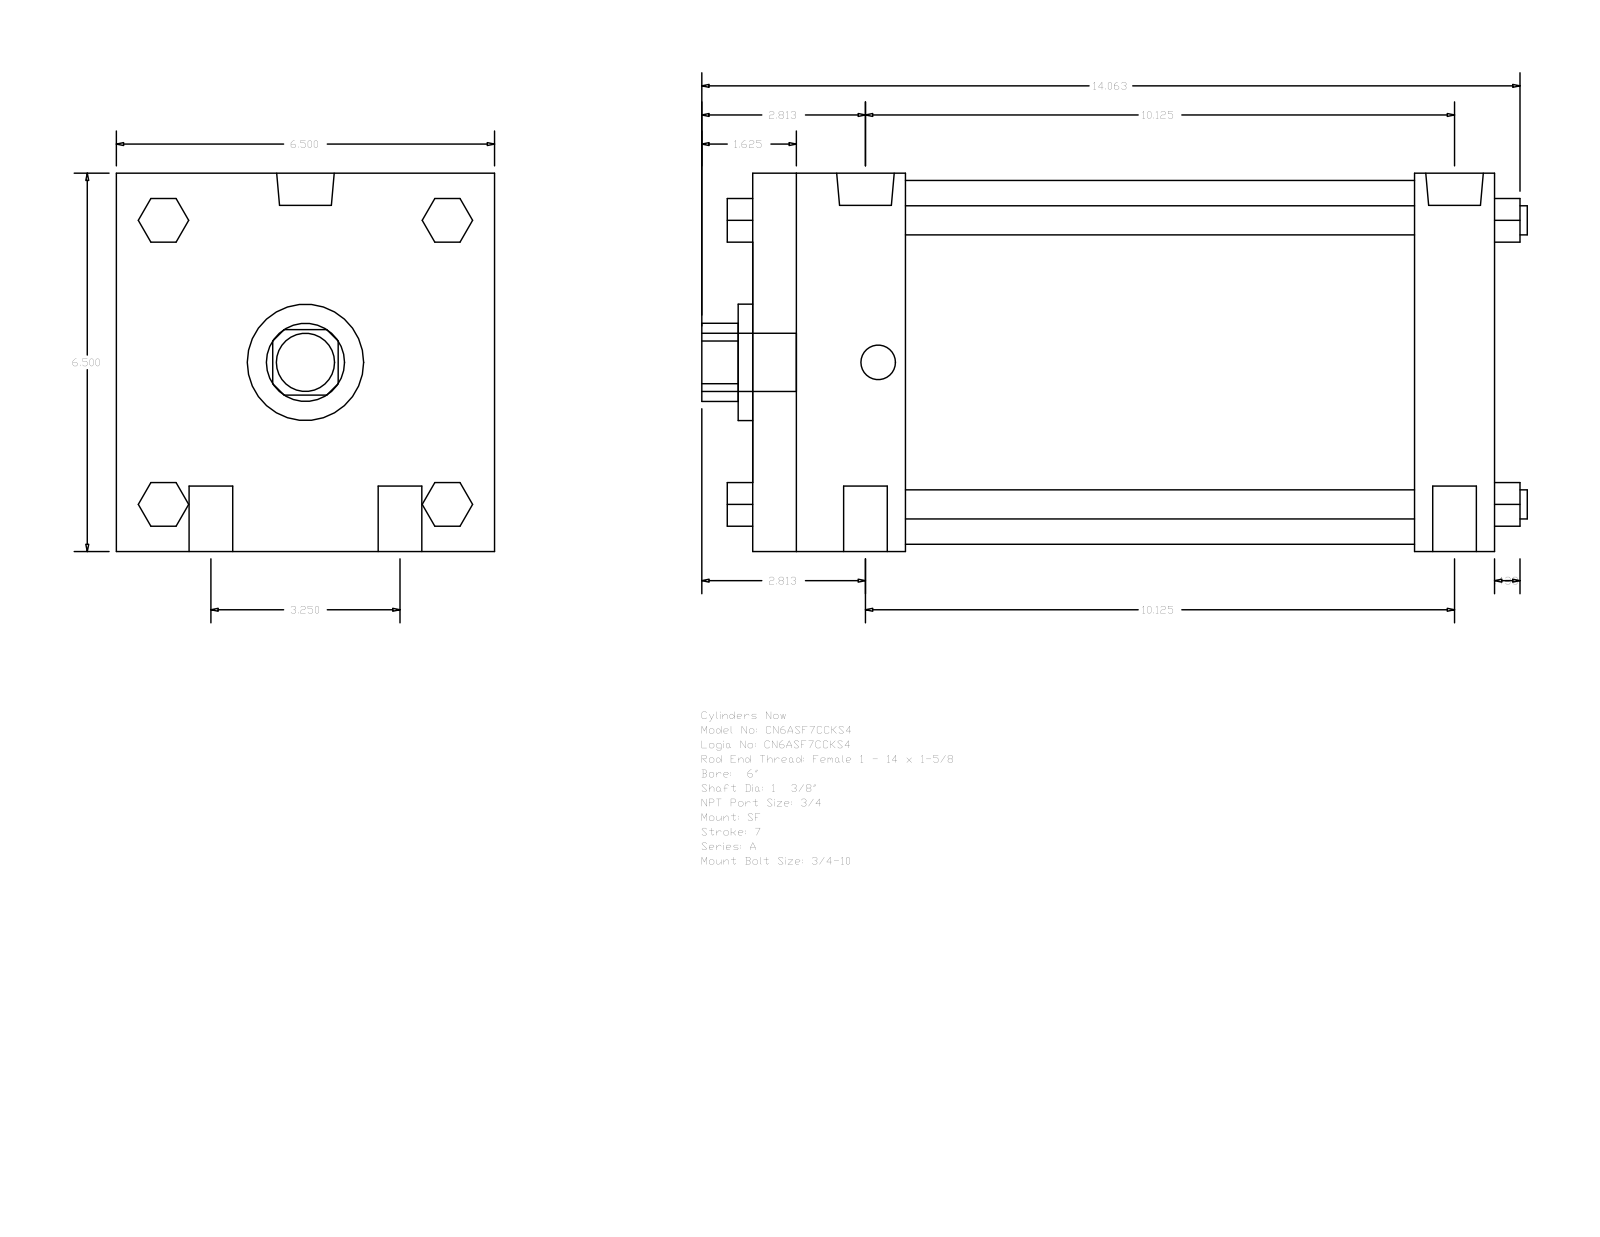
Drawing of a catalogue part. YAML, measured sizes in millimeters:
part_name: "A_SF__0600_1.375"
step_written_by: "GSSL Pune (CONFIG_CONTROL_DESIGN)"
units: millimeters
bodies: {solids: 0, faces: 124, planar: 94, cylindrical: 30, other: 0}
overall_size: [360.36, 165.1, 165.1]
round_holes:
  - {diameter: 34.92, count: 1}
  - {diameter: 50.8, count: 1}
  - {diameter: 158.75, count: 1}
round_bosses_or_shafts:
  - {diameter: 19.05, count: 4}
  - {diameter: 12.7, count: 4}
  - {diameter: 25.12, count: 2}
  - {diameter: 15.08, count: 2}
  - {diameter: 25.4, count: 1}
partial_cylinders:
  - {radius: 17.06, count: 1}
face_to_face_distances: [165.1, 323.84, 288.92, 34.92, 66.67, 222.25, 257.17, 19.05, 61.97, 107.34]
